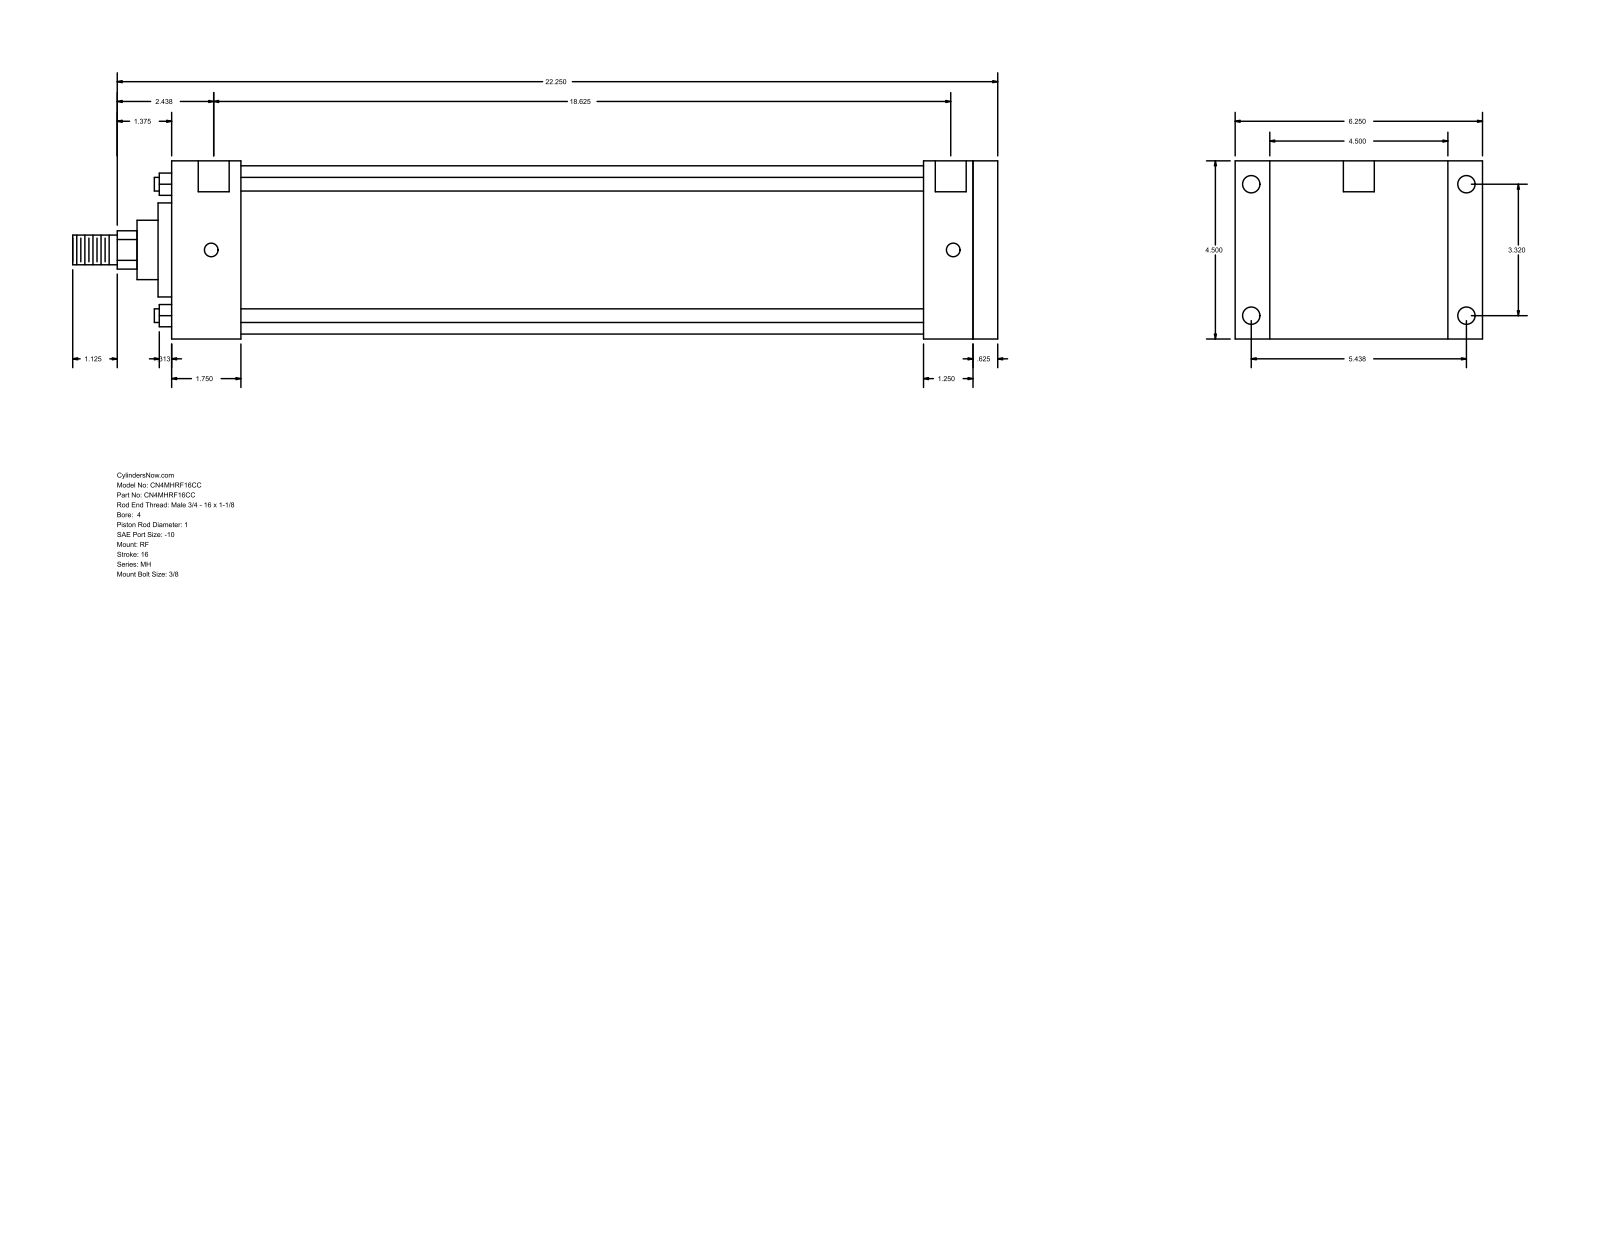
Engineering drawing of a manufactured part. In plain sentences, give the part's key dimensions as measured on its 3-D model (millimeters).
The part is named "MH_RF__0400_1". Its 3-D file was written by "GSSL Pune (CONFIG_CONTROL_DESIGN)". It is 0 solids with 94 faces: 65 planar, 29 cylindrical and 0 other. Overall it measures 593.73 by 158.75 by 114.3 millimeters. Round holes: 4 of diameter 8.73, 4 of diameter 11.13, 2 of diameter 19.84. Round bosses or shafts: 4 of diameter 8.76, 1 of diameter 107.95, 1 of diameter 60.33, 1 of diameter 38.1, 1 of diameter 25.4, 1 of diameter 19.05. Partial cylindrical surfaces (rounded edges, fillets, slot ends): 1 of radius 12.29. The main face-to-face distances are 114.3, 530.23, 514.35, 15.88, 47.63, 44.46, 469.89, 485.77, 482.6, 438.14. The hole center spacings are 84.32, 138.12, 161.82, 476.25, 1.58, 1.59, 473.08, 474.66.
